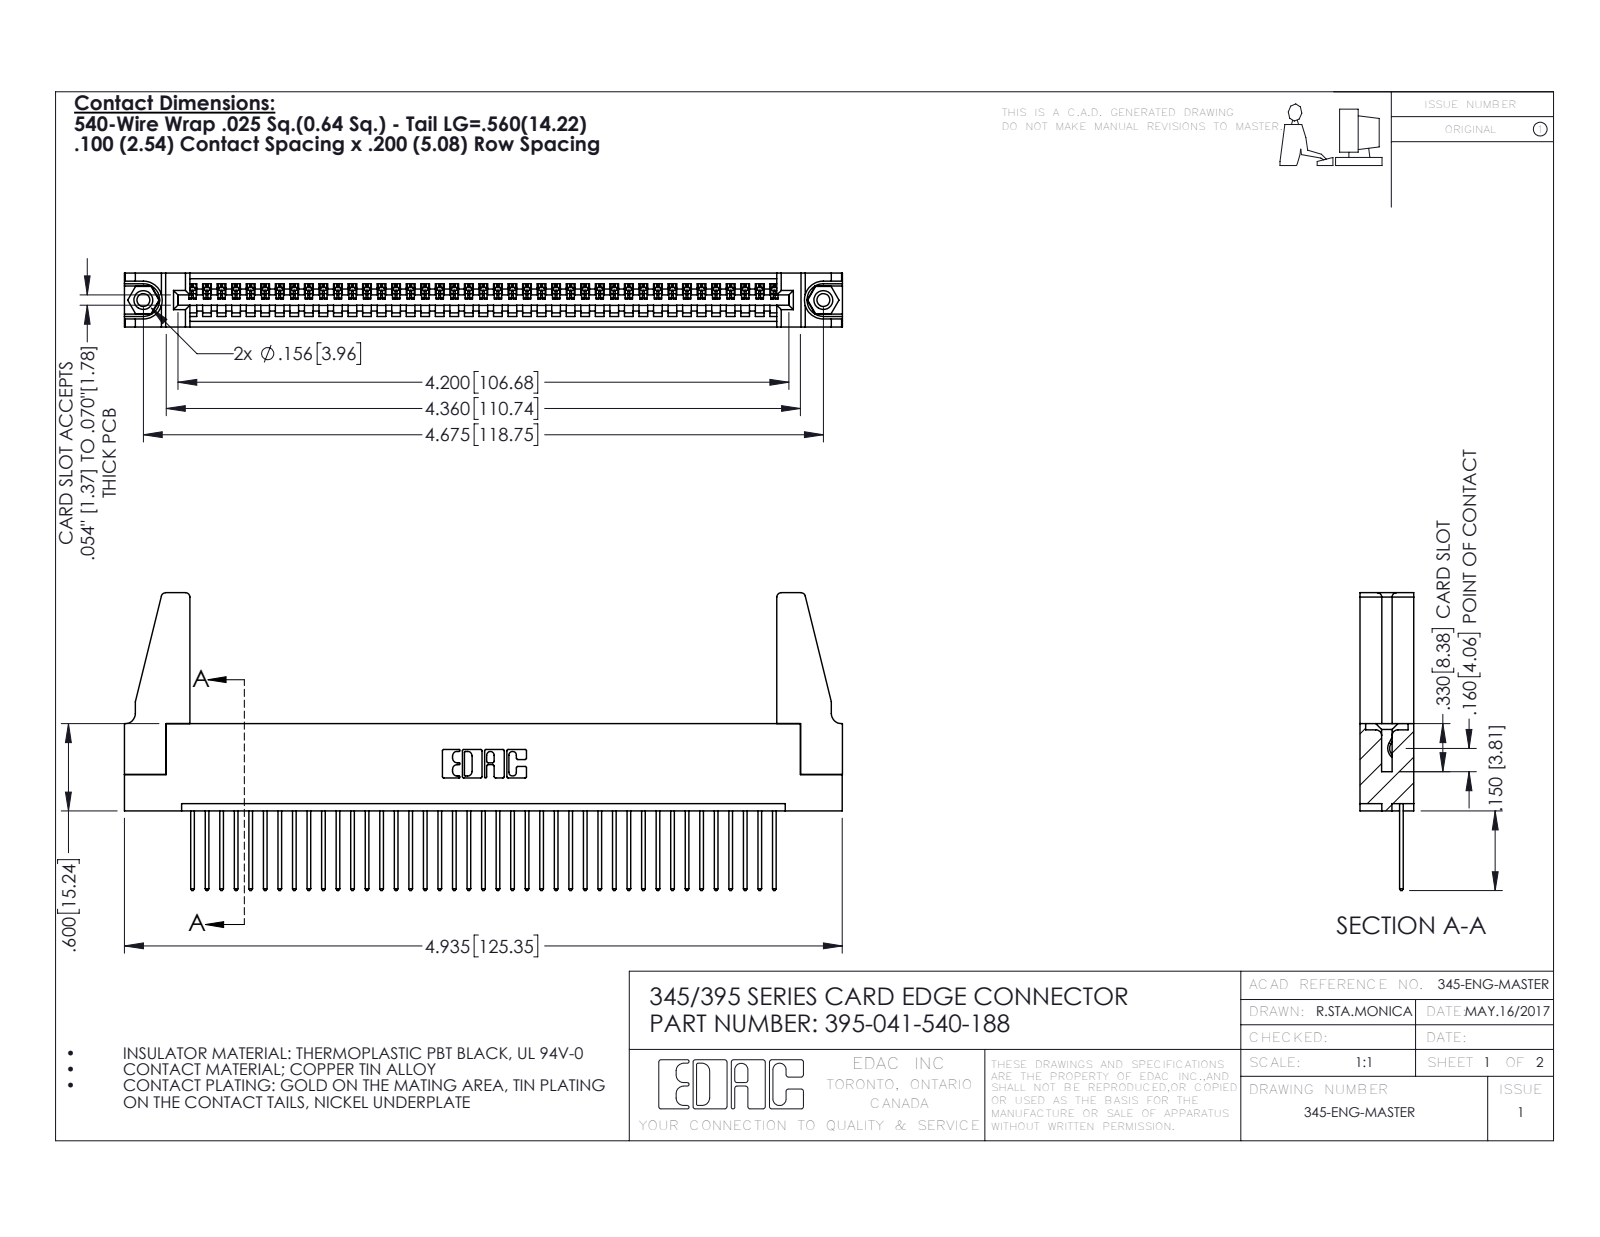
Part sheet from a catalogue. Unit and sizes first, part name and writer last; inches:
Units: inches
Overall size (bounding box): 4.936 × 2.047 × 0.37
Round holes (diameter × count): ⌀0.089 ×2, ⌀0.125 ×2, ⌀0.156 ×2, ⌀0.064 ×1
Round bosses / shafts (diameter × count): ⌀0.155 ×2
Partial cylindrical surfaces — rounded edges, fillets, slot ends (radius × count): R0.006 ×82, R0.01 ×82, R0.01 ×22, R0.03 ×8, R0.007 ×6, R0.031 ×6, R0.026 ×3, R0.031 ×2
Main face-to-face distances: 0.072, 0.298, 0.37, 0.2, 0.098, 0.272, 0.025, 0.225, 0.149, 0.072
Hole centre spacings: 0.27, 4.439, 4.675
Volume: 0.928 in³ · Surface area: 30.07 in²
Bodies: 46 solids, 2628 faces (1792 planar, 820 cylindrical, 16 other)
Part name (STEP PRODUCT): 345-220-078_345-220-088; 345 Part_Flush Mounting Lugs - 0.156 Dia-TH; 345-250-001_345-250-001-102; 345-292-001_345-293-140 (+1 more)
STEP written by: SolidWorks 2016 (CONFIG_CONTROL_DESIGN)
